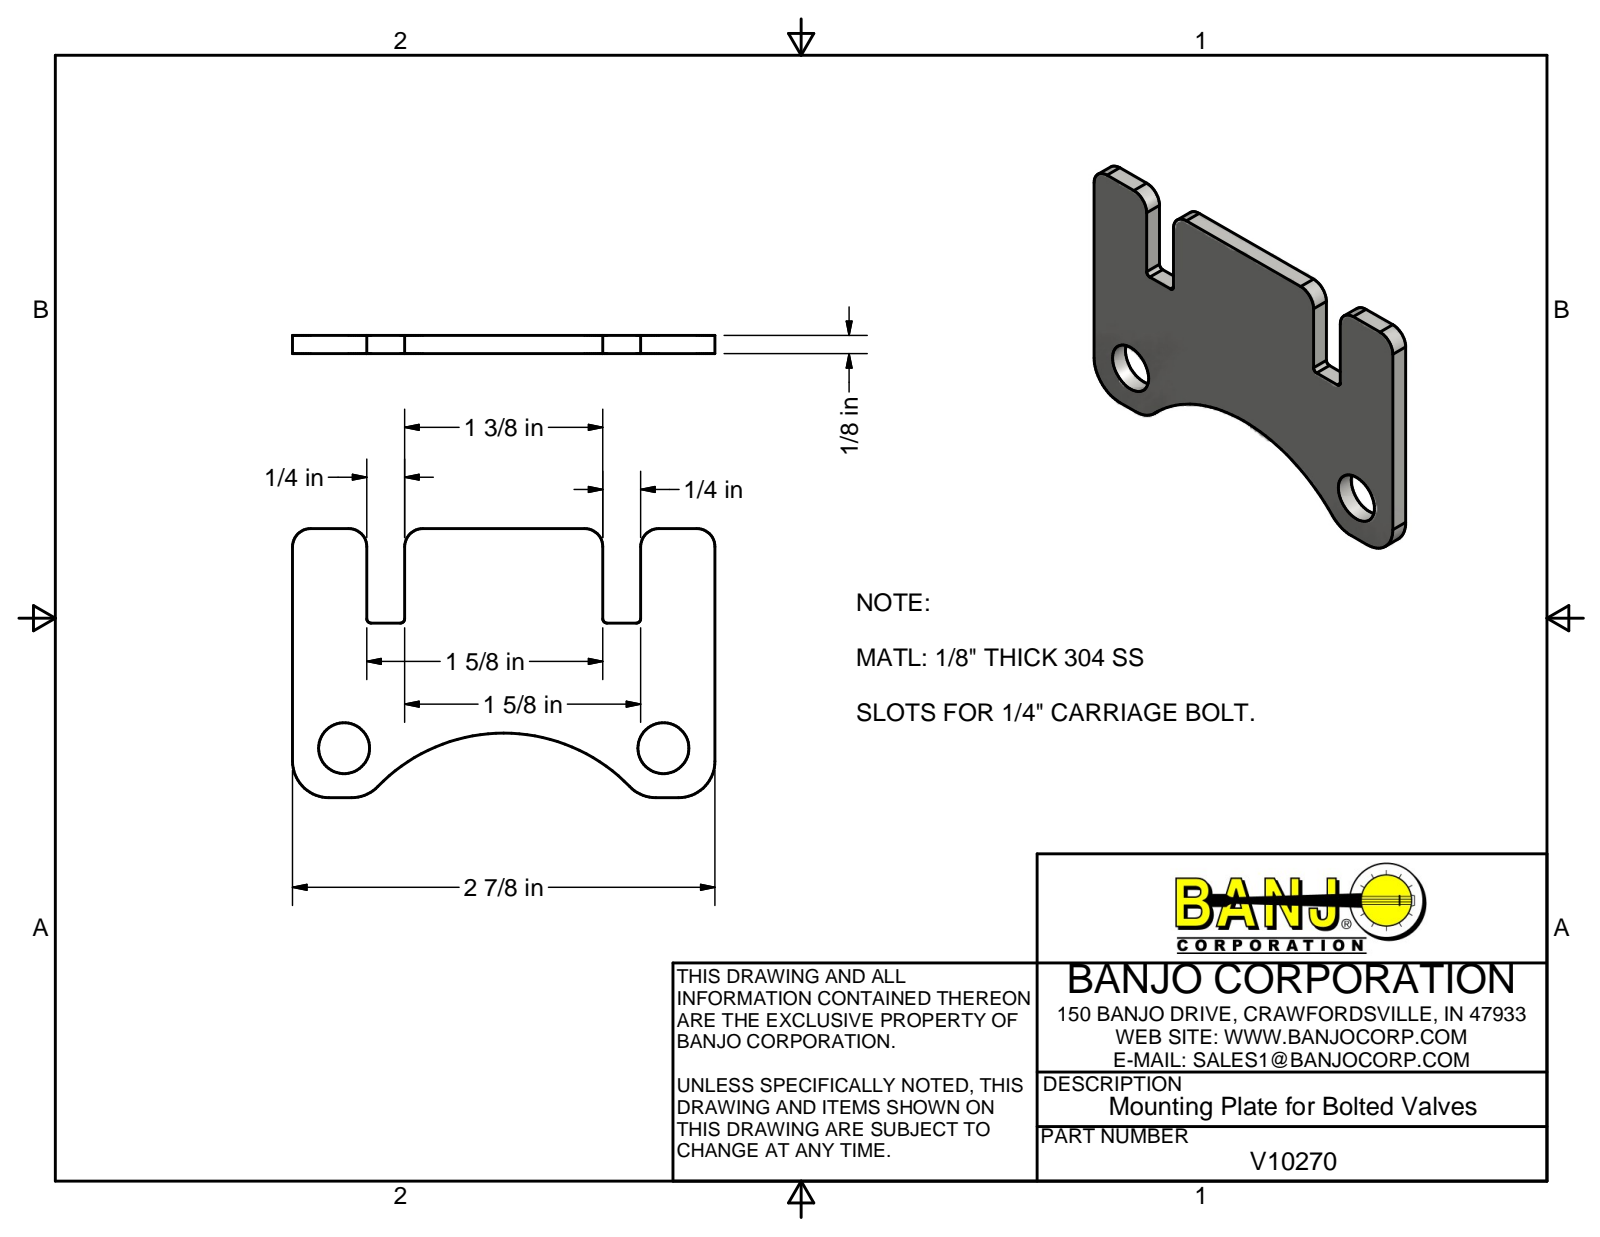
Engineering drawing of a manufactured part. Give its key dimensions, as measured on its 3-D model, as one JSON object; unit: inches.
{"part_name": "V10270", "step_written_by": "Autodesk Inventor 2013 (AUTOMOTIVE_DESIGN)", "units": "inches", "bodies": {"solids": 1, "faces": 32, "planar": 15, "cylindrical": 17, "other": 0}, "overall_size": [2.9, 1.85, 0.125], "volume_in3": 0.526, "surface_area_in2": 10.16, "round_holes": [[0.35, 2]], "partial_cylinders_radius": [[0.125, 6], [0.03, 4], [0.25, 4], [1.2, 1]], "face_to_face_distances": [0.125, 2.9, 0.51, 0.77, 2.13, 2.39, 0.26, 1.62, 1.88, 1.36], "hole_center_spacings": [2.192]}
